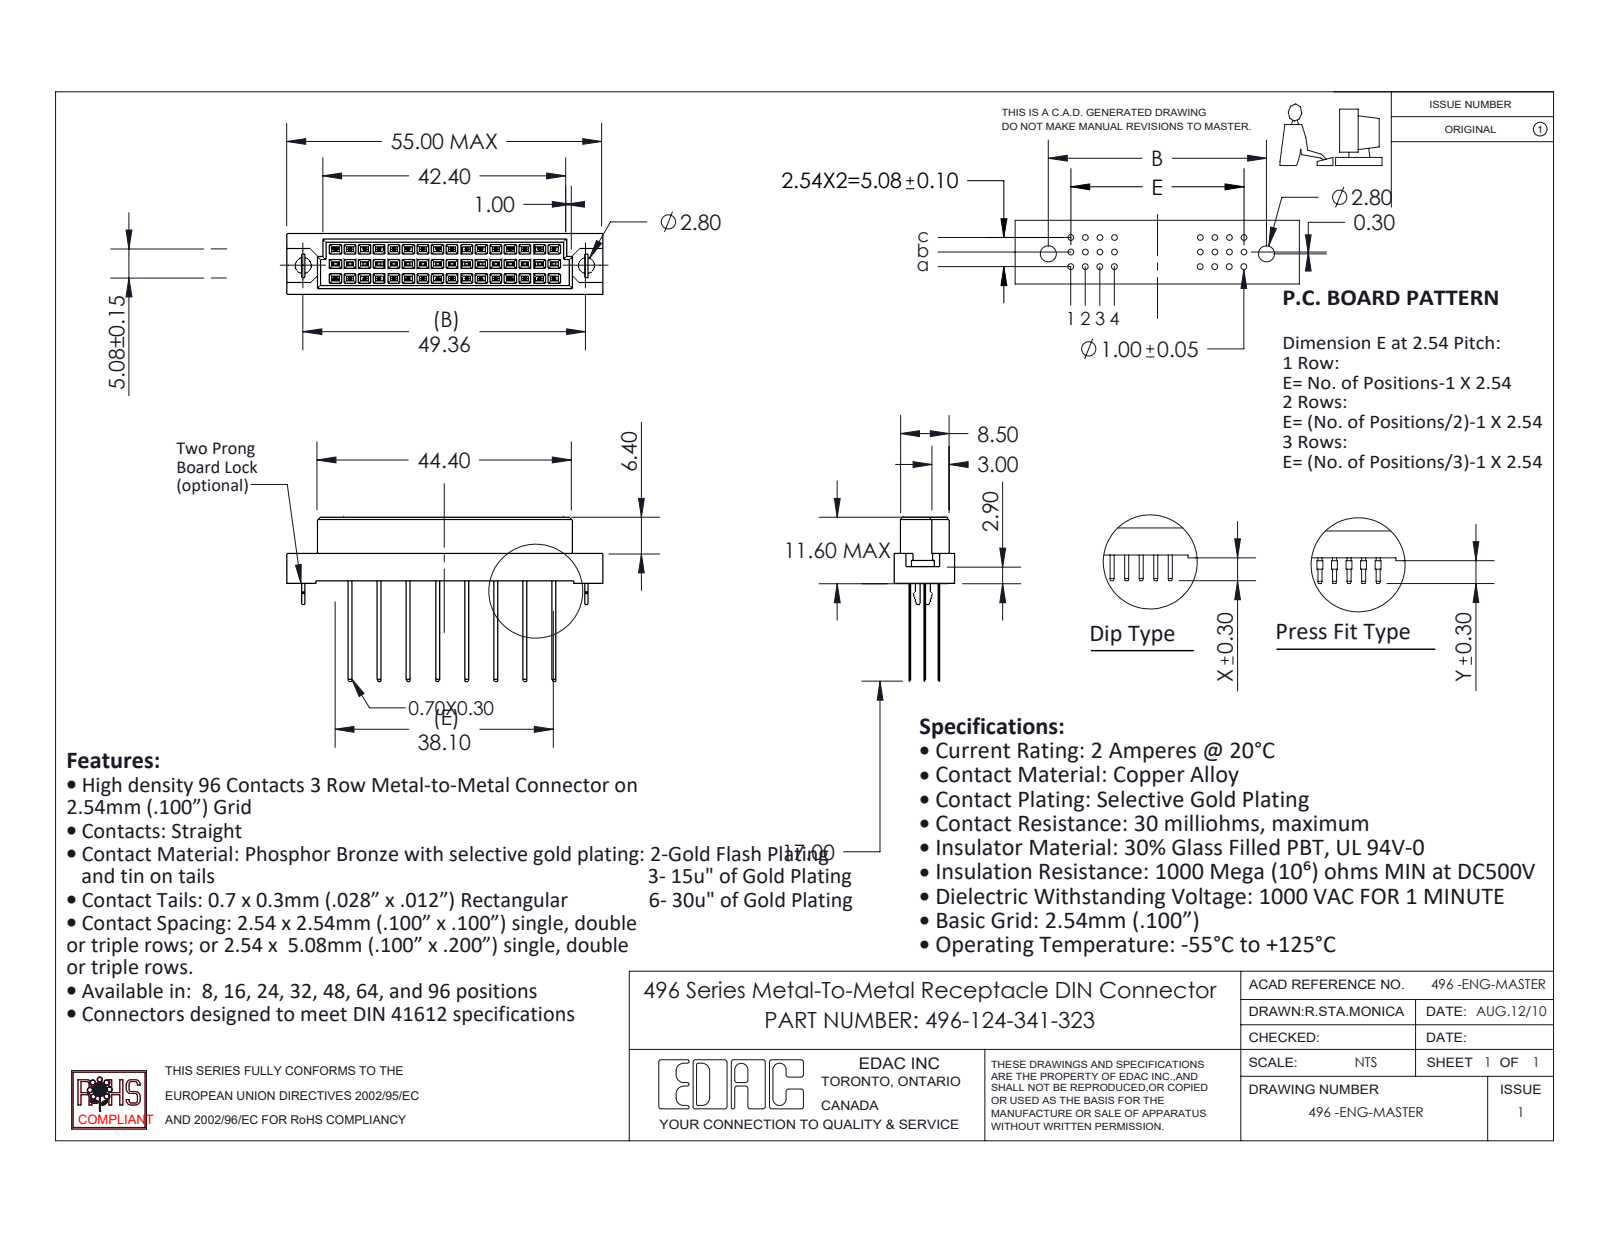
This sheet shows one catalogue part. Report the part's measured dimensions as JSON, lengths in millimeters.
{"part_name": "496 Part_48; 496 Bore-lock; 496-290_41; 496-124-341-323", "step_written_by": "SolidWorks 2020 (CONFIG_CONTROL_DESIGN)", "units": "millimeters", "bodies": {"solids": 27, "faces": 942, "planar": 936, "cylindrical": 6, "other": 0}, "overall_size": [55, 28.6, 10.6], "volume_mm3": 4719, "surface_area_mm2": 5356, "round_holes": [[2.8, 2]], "partial_cylinders_radius": [[0.53, 1]], "face_to_face_distances": [2.54, 5.08, 1.05, 9.55, 0.56, 0.55, 0.81, 2.84, 1.56, 1.86], "hole_center_spacings": [49.36]}
